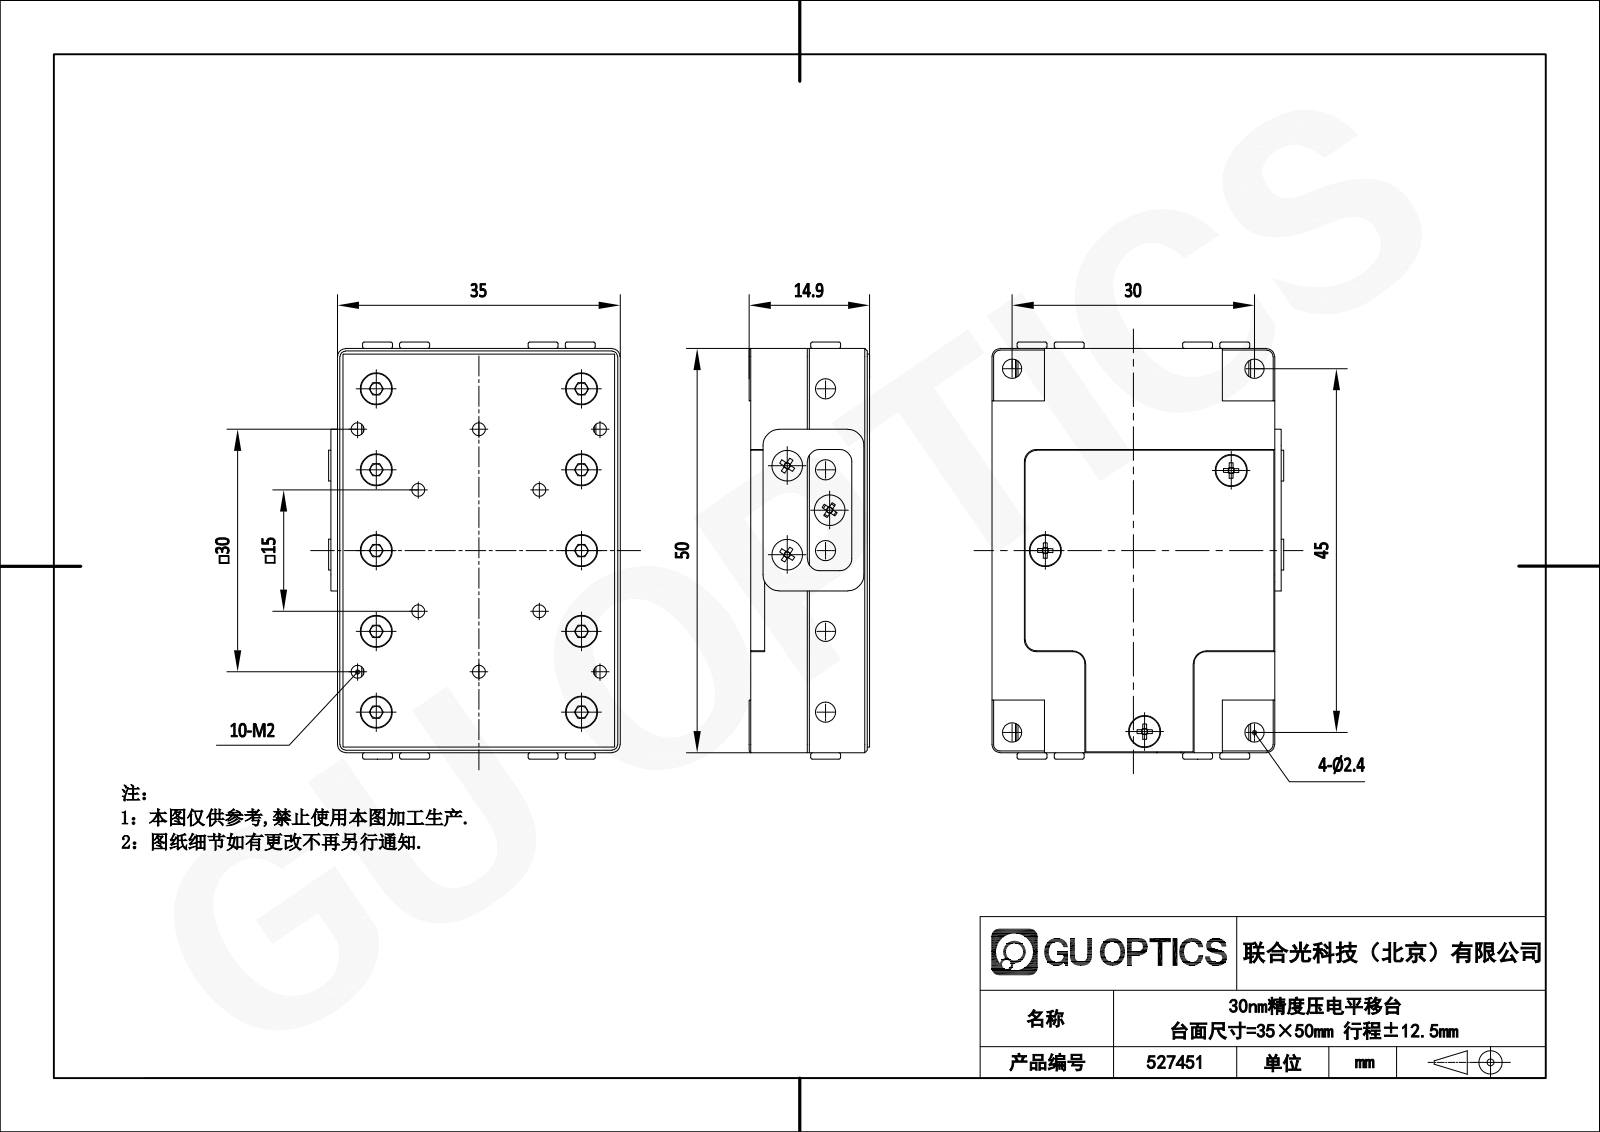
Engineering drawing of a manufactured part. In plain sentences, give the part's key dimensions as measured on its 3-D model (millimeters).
The part is named "socket head cap screw_din_DIN 912 M2 x 3 --- 3N.STEP; LS1-0310__________.STEP; countersunk flat head cross recess screw_din_DIN EN ISO 7046-1 - M2 x 3 - Z - 3N.STEP; 527451-527471.STEP (+6 more)". Its 3-D file was written by "SolidWorks 2020 (CONFIG_CONTROL_DESIGN)". It is 24 solids with 1001 faces: 479 planar, 294 cylindrical and 228 other. Overall it measures 51.6 by 36.1 by 14.9 millimeters. Its volume is 24 162 cubic millimeters and its surface area 18 784 square millimeters. Round holes: 20 of diameter 1.65, 20 of diameter 3, 17 of diameter 4, 14 of diameter 2.4, 13 of diameter 1.6, 5 of diameter 2.2, 5 of diameter 2.5. Round bosses or shafts: 16 of diameter 3.8, 16 of diameter 2, 4 of diameter 3.7. Partial cylindrical surfaces (rounded edges, fillets, slot ends): 8 of radius 1.5, 6 of radius 1, 4 of radius 2, 2 of radius 1.4, 2 of radius 1.6. The main face-to-face distances are 11.5, 13, 1.7, 14.7, 4.25, 4, 3.45, 9.55, 11.25, 3.2. The hole center spacings are 10, 11.14, 22.81, 20, 30, 20.59, 28.64, 4.9.
